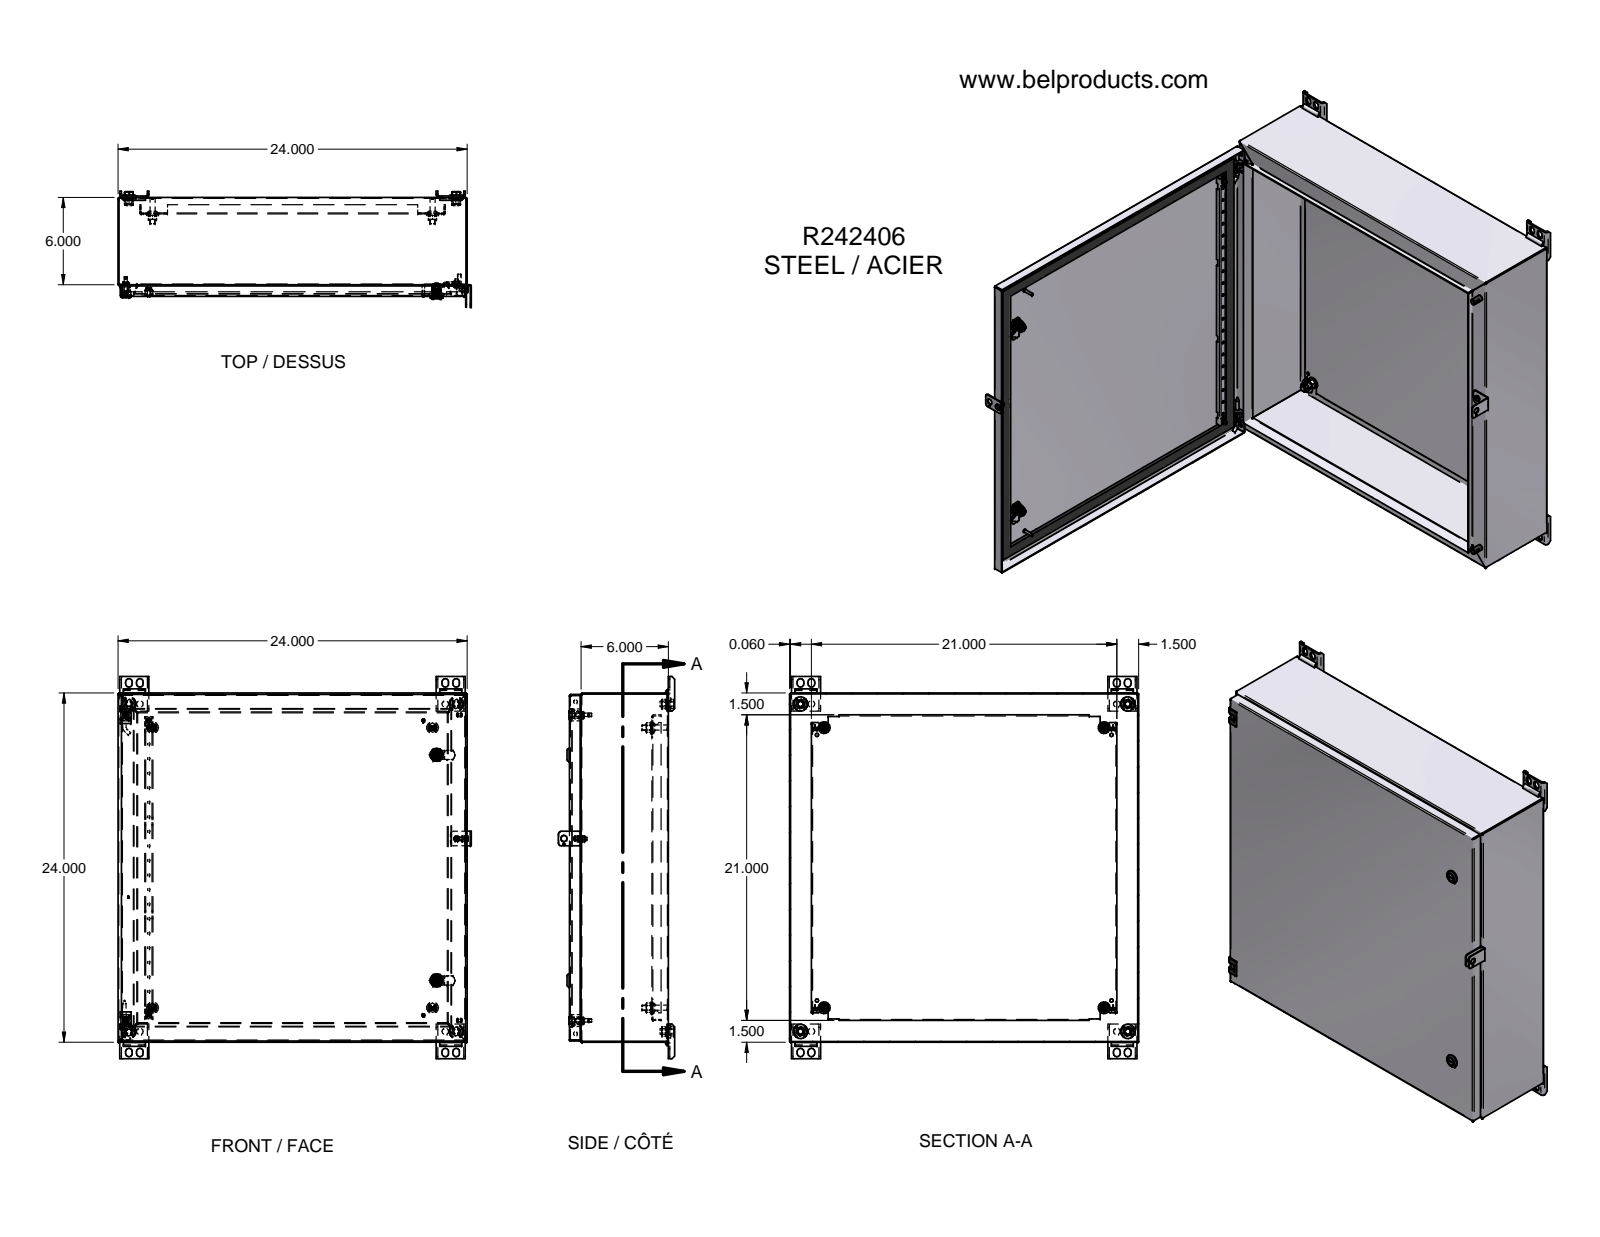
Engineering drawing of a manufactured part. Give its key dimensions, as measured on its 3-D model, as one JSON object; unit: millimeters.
{"part_name": "LOCK AVEC TOURNEVIS TYPE 4-12 SANS CAME; HOSING-oa0; INSERT POUR TOURNEVIS-oa1; NOIX DE FIXATION-oa2 (+8 more)", "step_written_by": "Unknown (AUTOMOTIVE_DESIGN)", "units": "millimeters", "bodies": {"solids": 88, "faces": 3590, "planar": 2052, "cylindrical": 638, "other": 900}, "overall_size": [667.16, 616.76, 203.07], "volume_mm3": 2892000, "surface_area_mm2": 3371000, "round_holes": [[4.68, 20], [3.17, 10], [9.53, 8], [10.31, 8], [11.58, 8], [0.35, 6], [4.04, 4], [5.99, 4], [6.73, 4], [9.02, 4], [10.54, 4], [12.7, 4]], "round_bosses_or_shafts": [[3.02, 10], [20.62, 8], [4.83, 5], [16.19, 4], [8.97, 4], [6.5, 4], [0.79, 4], [0.51, 4]], "partial_cylinders_radius": [[0.2, 84], [0.81, 28], [9.53, 22], [0.3, 18], [2.34, 18], [0.25, 16], [5.79, 16], [4.76, 12]], "face_to_face_distances": [1.52, 170.98, 169.46, 172.5, 608.08, 1.91, 143.77, 142.25, 27.21, 28.73], "hole_center_spacings": [25.4, 50.8, 76.2, 101.6, 127, 152.4, 177.8, 203.2]}
